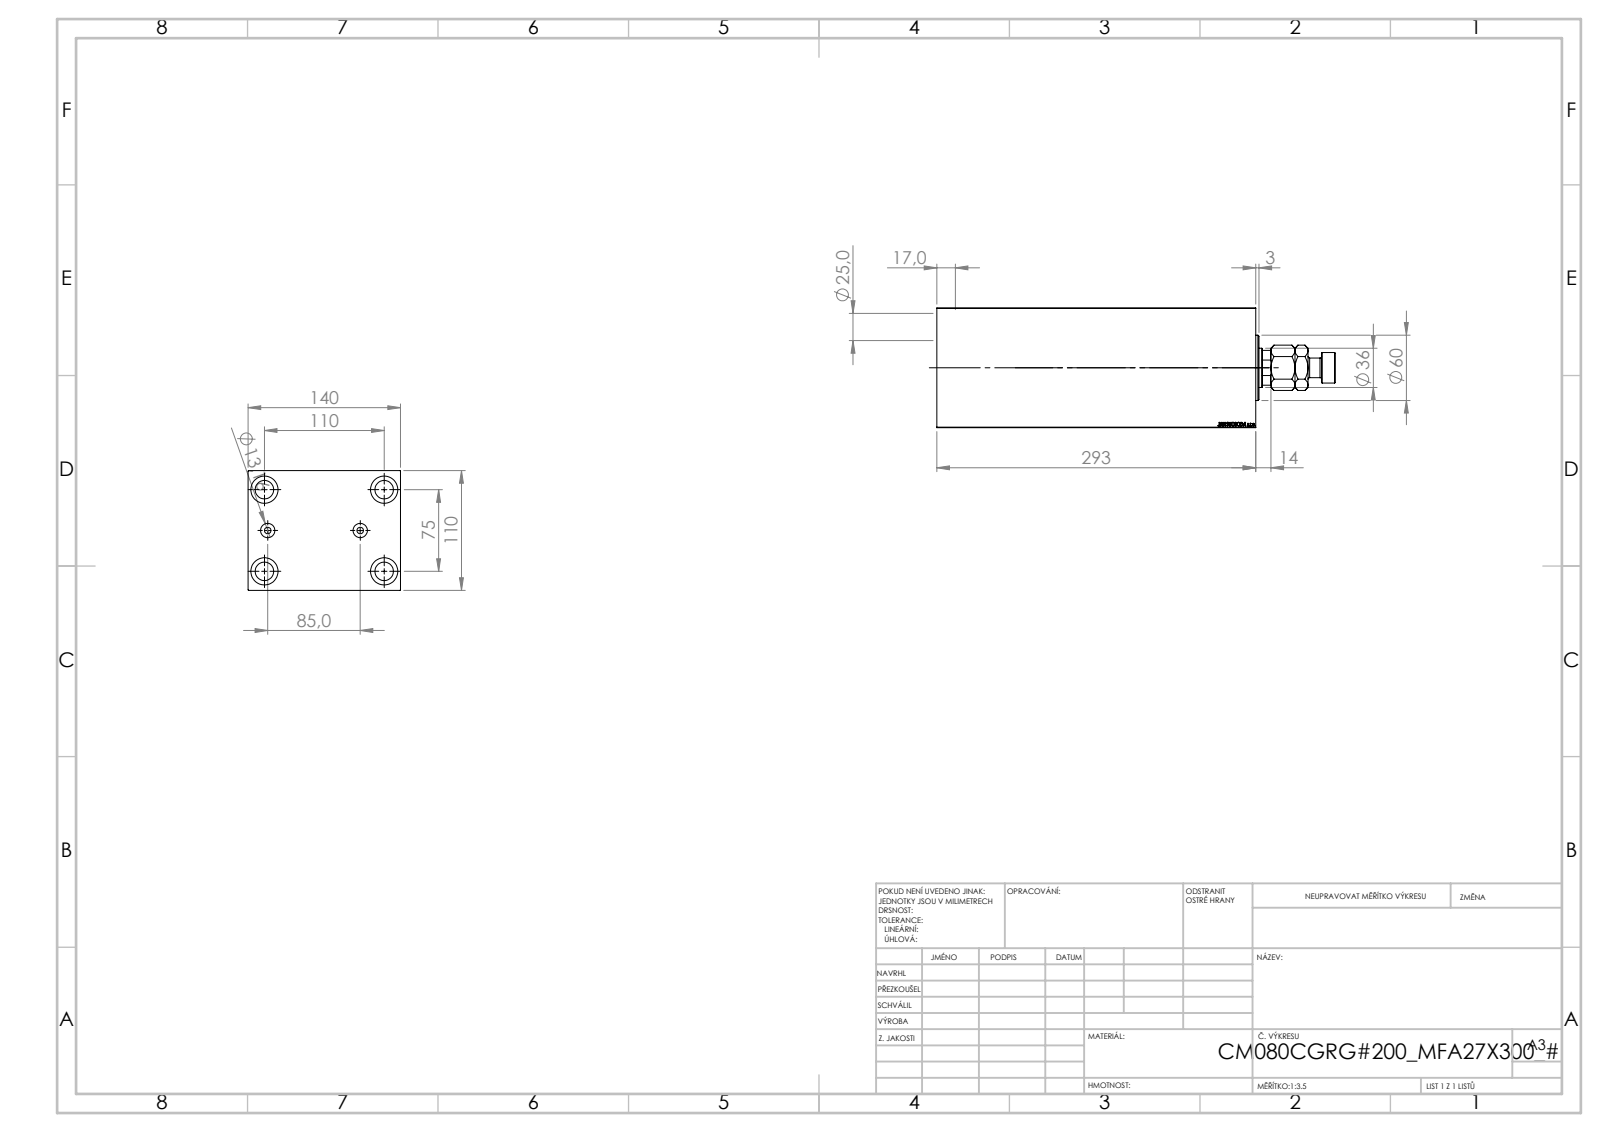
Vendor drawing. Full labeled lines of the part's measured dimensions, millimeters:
Part name (STEP PRODUCT): V450CM_VC_B; MFA; V450CM_C_VCP; V450CM_C_Body
STEP written by: SolidWorks 2019 (CONFIG_CONTROL_DESIGN)
Units: millimetres
Bodies: 4 solids, 915 faces (427 planar, 62 cylindrical, 426 other)
Overall size (bounding box): 366 × 140 × 110
Volume: 3 440 000 mm³ · Surface area: 400 331 mm²
Round holes (diameter × count): ⌀17 ×4, ⌀25 ×4, ⌀6 ×2, ⌀13.16 ×2, ⌀25.5 ×1, ⌀36 ×1, ⌀39.5 ×1, ⌀80 ×1, ⌀82 ×1, ⌀87 ×1
Round bosses / shafts (diameter × count): ⌀60 ×1, ⌀28 ×1, ⌀18 ×1
Partial cylindrical surfaces — rounded edges, fillets, slot ends (radius × count): R17.5 ×1
Main face-to-face distances: 110, 140, 293, 272, 21, 37.3, 234.7, 255.7, 237.3, 200
Hole centre spacings: 39.53, 66.57, 104.46, 42.5, 75, 110, 133.14, 85
